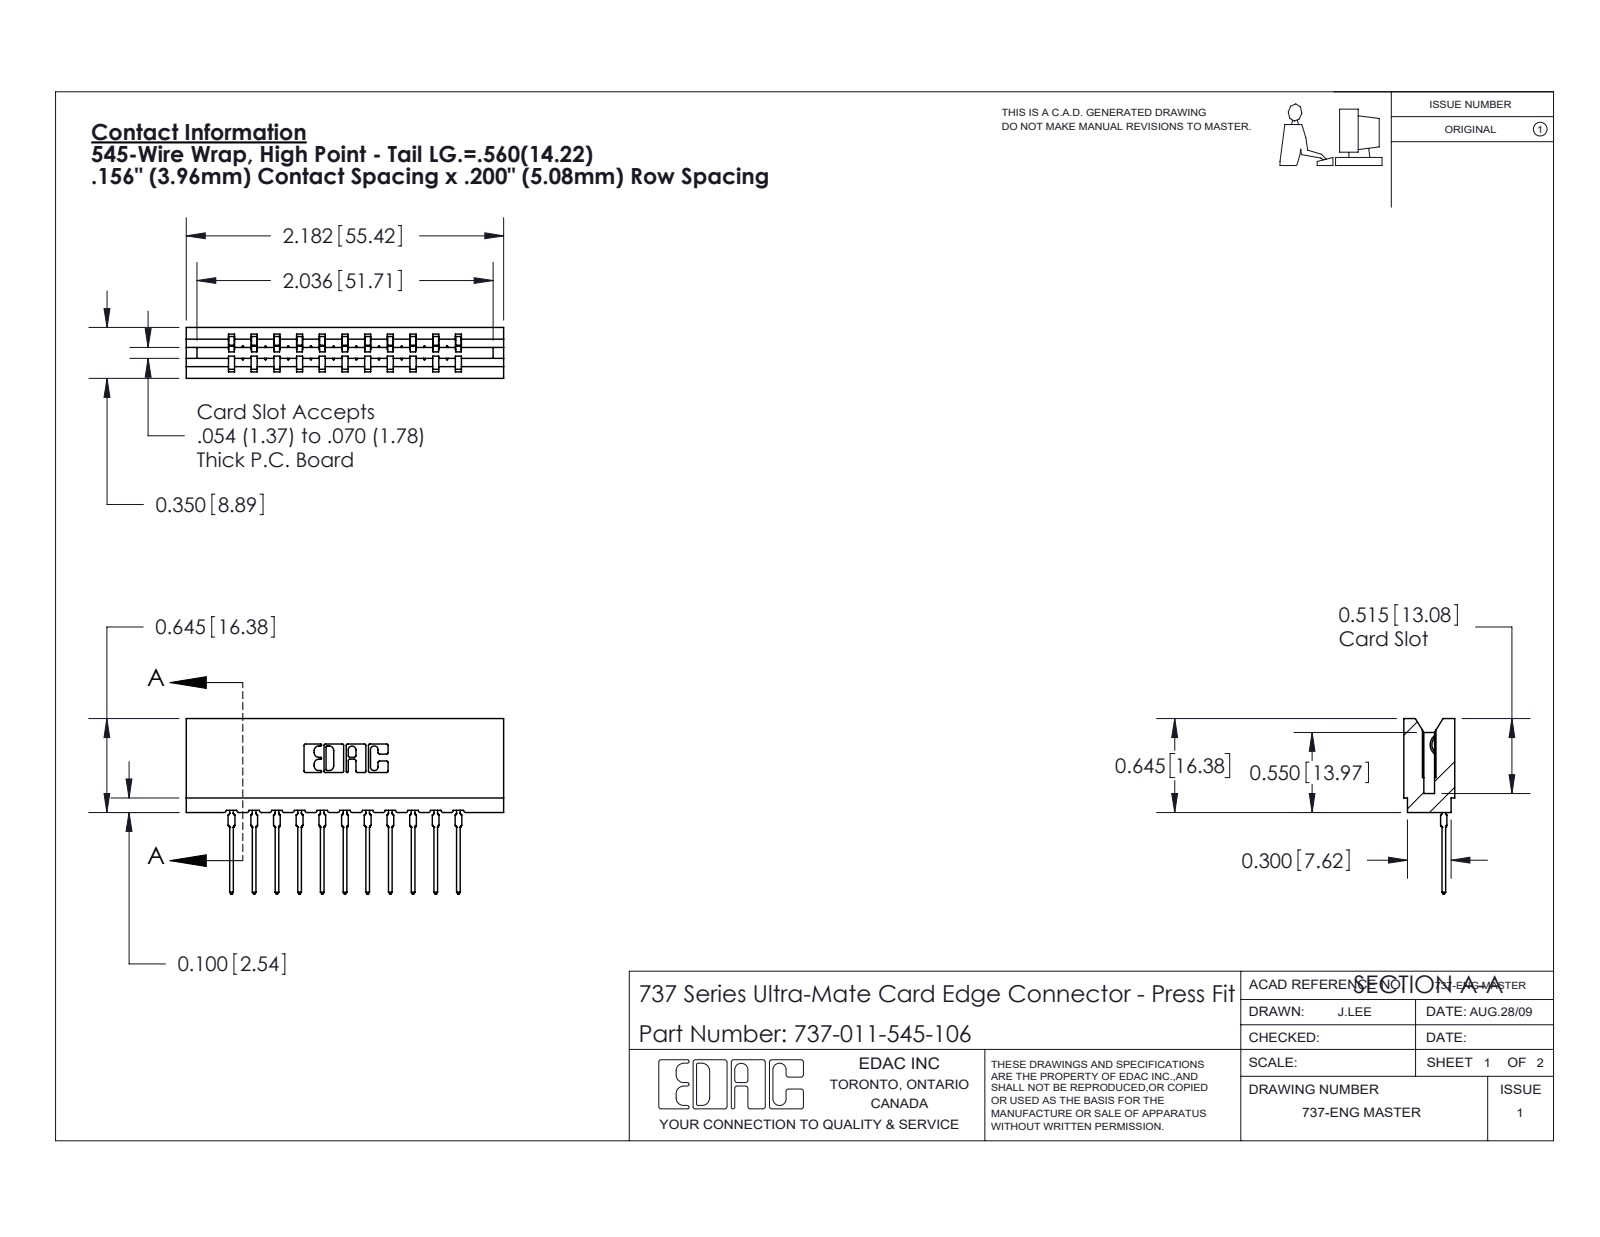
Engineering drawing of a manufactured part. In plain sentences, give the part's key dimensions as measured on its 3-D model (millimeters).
The part is named "737 Part_Insulator Option - 06; 745-292-001_545; 737-011-545-106". Its 3-D file was written by "SolidWorks 2020 (CONFIG_CONTROL_DESIGN)". It is 12 solids with 1338 faces: 803 planar, 249 cylindrical and 286 other. Overall it measures 55.4 by 30.6 by 8.9 millimeters. Its volume is 5 590 cubic millimeters and its surface area 7 116 square millimeters. Partial cylindrical surfaces (rounded edges, fillets, slot ends): 22 of radius 0.3, 22 of radius 0.4, 22 of radius 0.5, 6 of radius 0.2, 6 of radius 0.8, 4 of radius 0.1, 4 of radius 0.3, 3 of radius 0.7. The main face-to-face distances are 4, 3.5, 5.4, 8.9, 15.8, 9, 7.9, 19.8, 11.9, 1.9.
